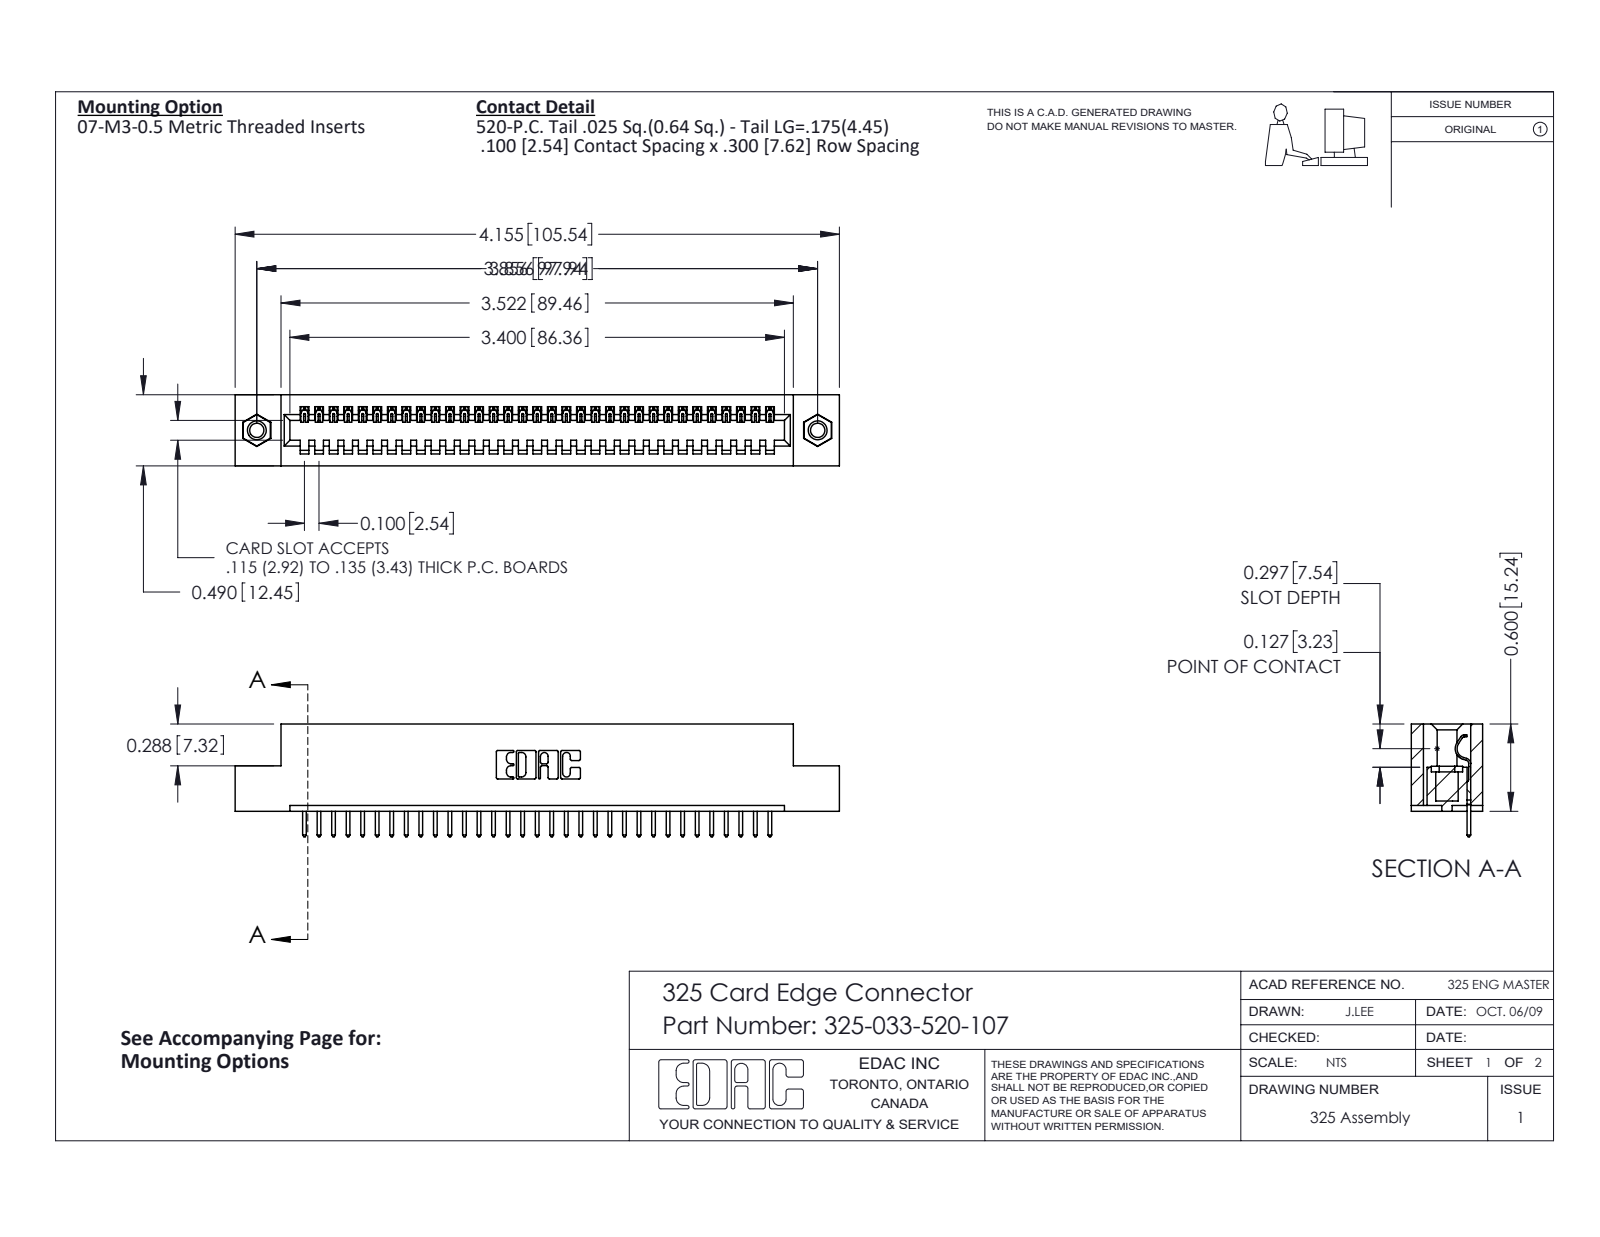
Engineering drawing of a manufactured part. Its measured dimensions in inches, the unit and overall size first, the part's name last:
Units: inches
Overall size (bounding box): 4.155 × 0.775 × 0.49
Round holes (diameter × count): ⌀0.098 ×2, ⌀0.125 ×2, ⌀0.16 ×2
Round bosses / shafts (diameter × count): ⌀0.155 ×2
Partial cylindrical surfaces — rounded edges, fillets, slot ends (radius × count): R0.006 ×66, R0.01 ×66, R0.01 ×22, R0.007 ×6, R0.031 ×6, R0.026 ×3, R0.014 ×1, R0.022 ×1
Main face-to-face distances: 0.083, 0.407, 0.49, 0.3, 0.107, 0.383, 0.025, 0.325, 0.56, 0.04
Hole centre spacings: 3.856
Volume: 0.807 in³ · Surface area: 21.67 in²
Bodies: 36 solids, 2088 faces (1488 planar, 584 cylindrical, 16 other)
Part name (STEP PRODUCT): 325-292-001_325-293-120; 325-033-520-107; 345-250-001_345-250-005-103; 325 Part_TI
STEP written by: SolidWorks 2016 (CONFIG_CONTROL_DESIGN)
